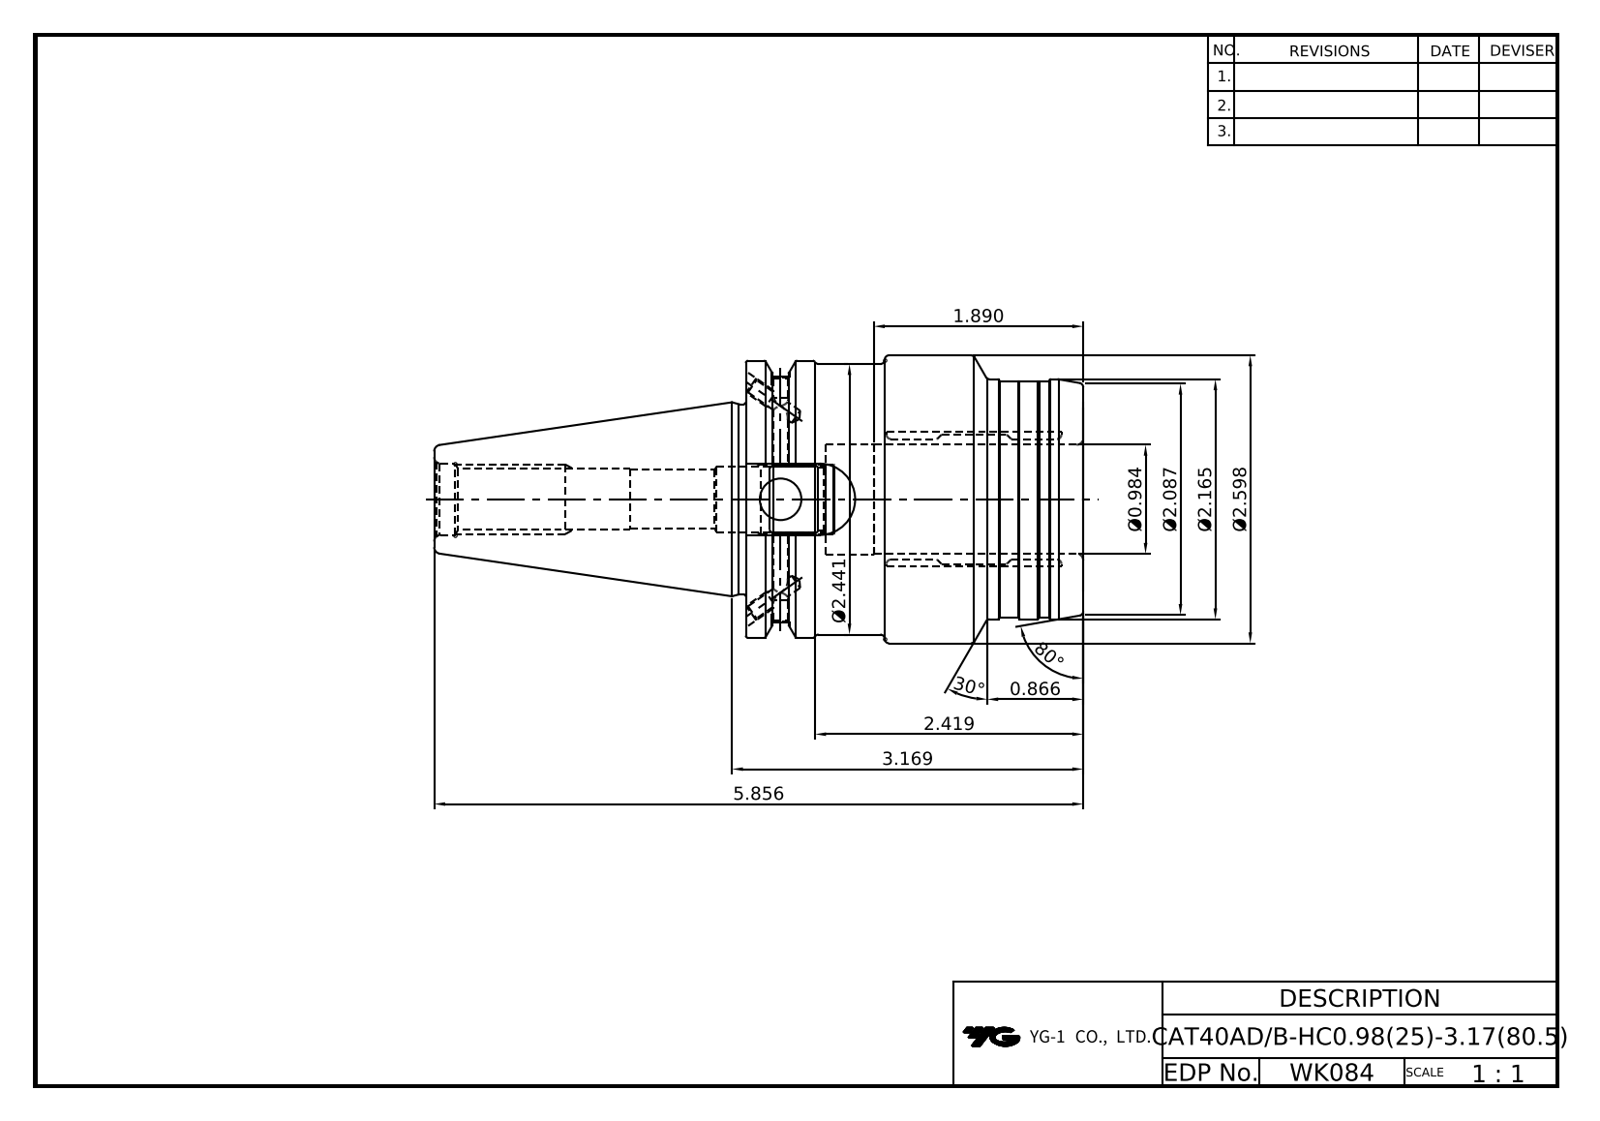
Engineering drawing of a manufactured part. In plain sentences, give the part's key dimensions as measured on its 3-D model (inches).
The part is named "LO-CAT40ADB-HC25-80.5". Its 3-D file was written by "Autodesk Inventor 2025 (AUTOMOTIVE_DESIGN)". It is 1 solid with 106 faces: 32 planar, 36 cylindrical and 38 other. Overall it measures 5.856 by 2.598 by 2.598 inches. Its volume is 15.05 cubic inches and its surface area 58.83 square inches. Round holes: 4 of diameter 0.128, 2 of diameter 0.157, 2 of diameter 0.165, 1 of diameter 0.375, 1 of diameter 0.527, 1 of diameter 0.587, 1 of diameter 0.642, 1 of diameter 0.984, 1 of diameter 1.008. Round bosses or shafts: 1 of diameter 2.598, 1 of diameter 2.5, 1 of diameter 2.441, 1 of diameter 2.165, 1 of diameter 2.126, 1 of diameter 1.717. Partial cylindrical surfaces (rounded edges, fillets, slot ends): 1 of radius 0.322, 1 of radius 1.108. The main face-to-face distances are 3.044, 0.722, 2.323, 1.874, 0.645, 2.812, 3.533, 5.856, 3.201, 0.389.
